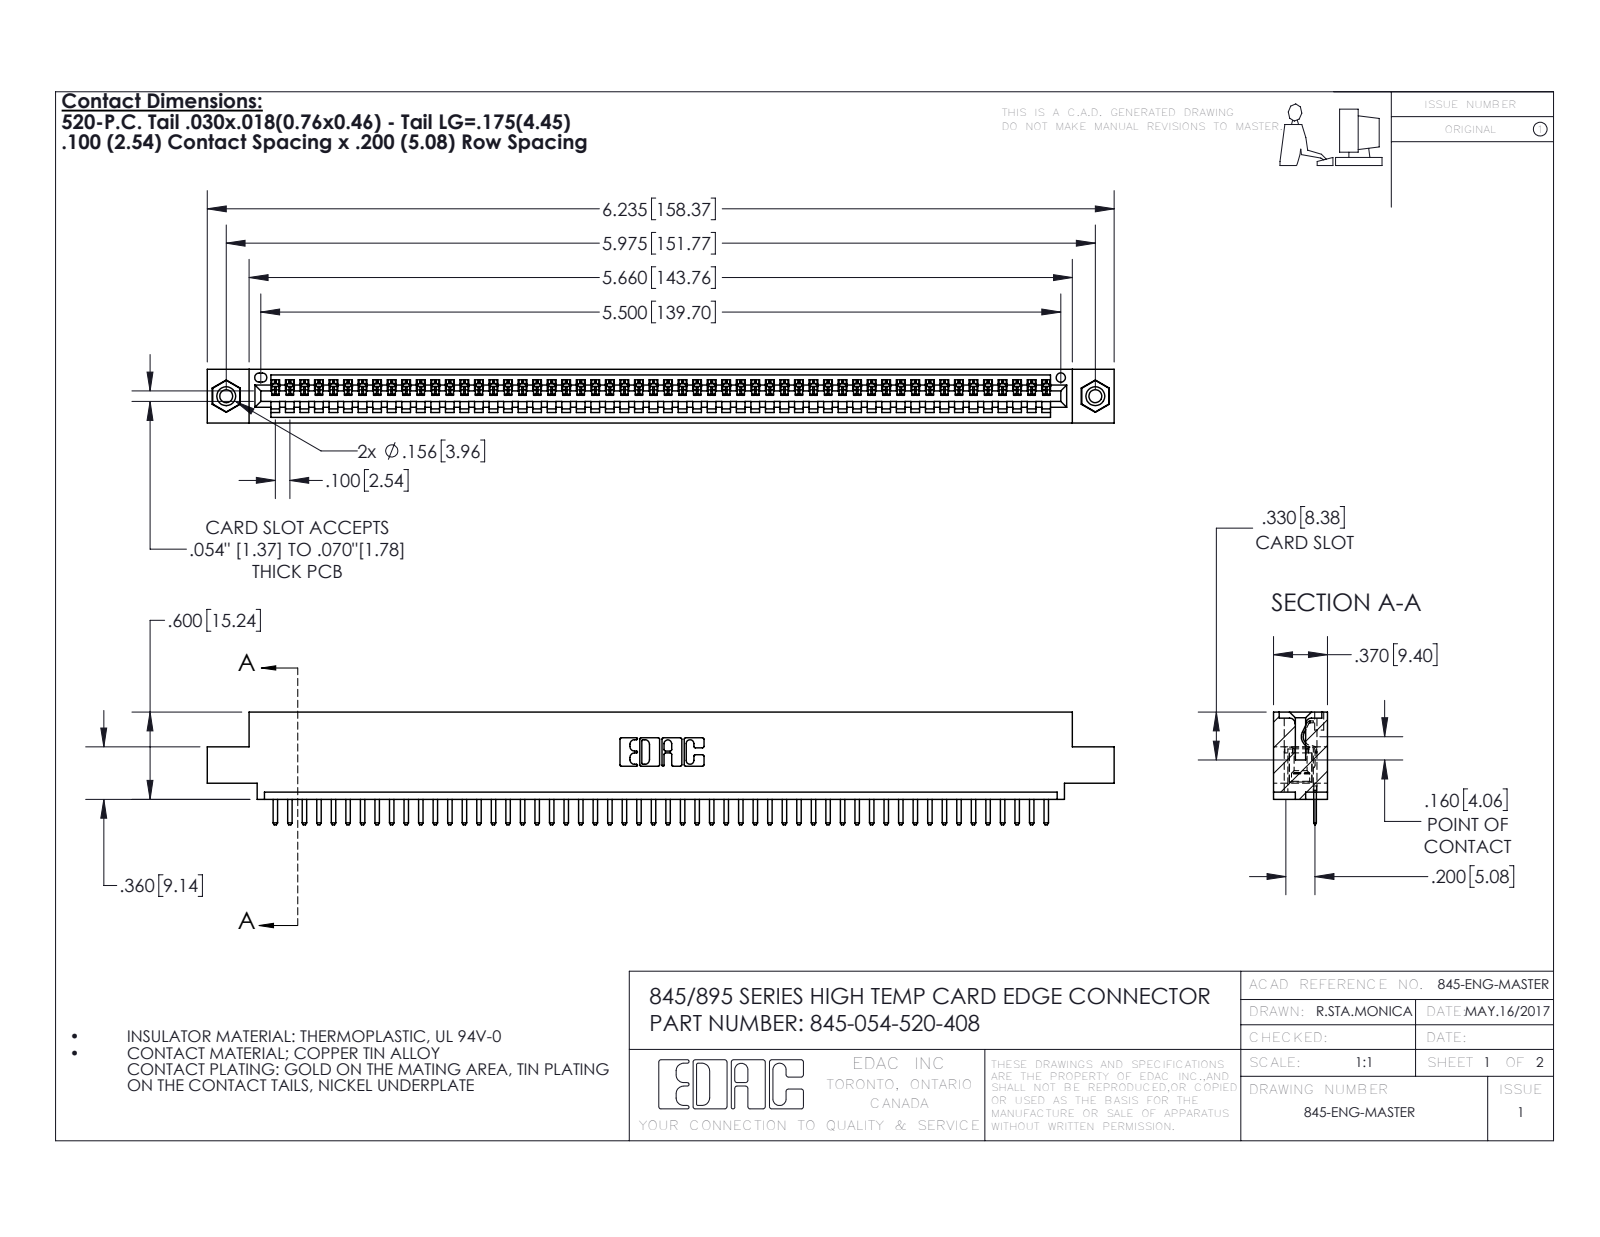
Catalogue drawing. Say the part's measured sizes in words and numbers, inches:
The part is named "345 Part_0.110 Offset - 0.156 Dia-TI; 345-054-520-408; 345-292-001_345-293-120; 345-250-001_345-250-003-102". Its 3-D file was written by "SolidWorks 2016 (CONFIG_CONTROL_DESIGN)". It is 57 solids with 3538 faces: 2384 planar, 1138 cylindrical and 16 other. Overall it measures 6.235 by 0.775 by 0.37 inches. Its volume is 0.91 cubic inches and its surface area 30.32 square inches. Round holes: 2 of diameter 0.089, 2 of diameter 0.125, 2 of diameter 0.156, 1 of diameter 0.064. Round bosses or shafts: 2 of diameter 0.155. Partial cylindrical surfaces (rounded edges, fillets, slot ends): 110 of radius 0.01, 108 of radius 0.006, 22 of radius 0.01, 6 of radius 0.007, 6 of radius 0.031, 3 of radius 0.026, 2 of radius 0.031, 2 of radius 0.04. The main face-to-face distances are 0.072, 0.298, 0.37, 0.2, 0.098, 0.272, 0.025, 0.225, 0.072, 0.149. The hole center spacings are 0.27, 5.739, 5.975.
